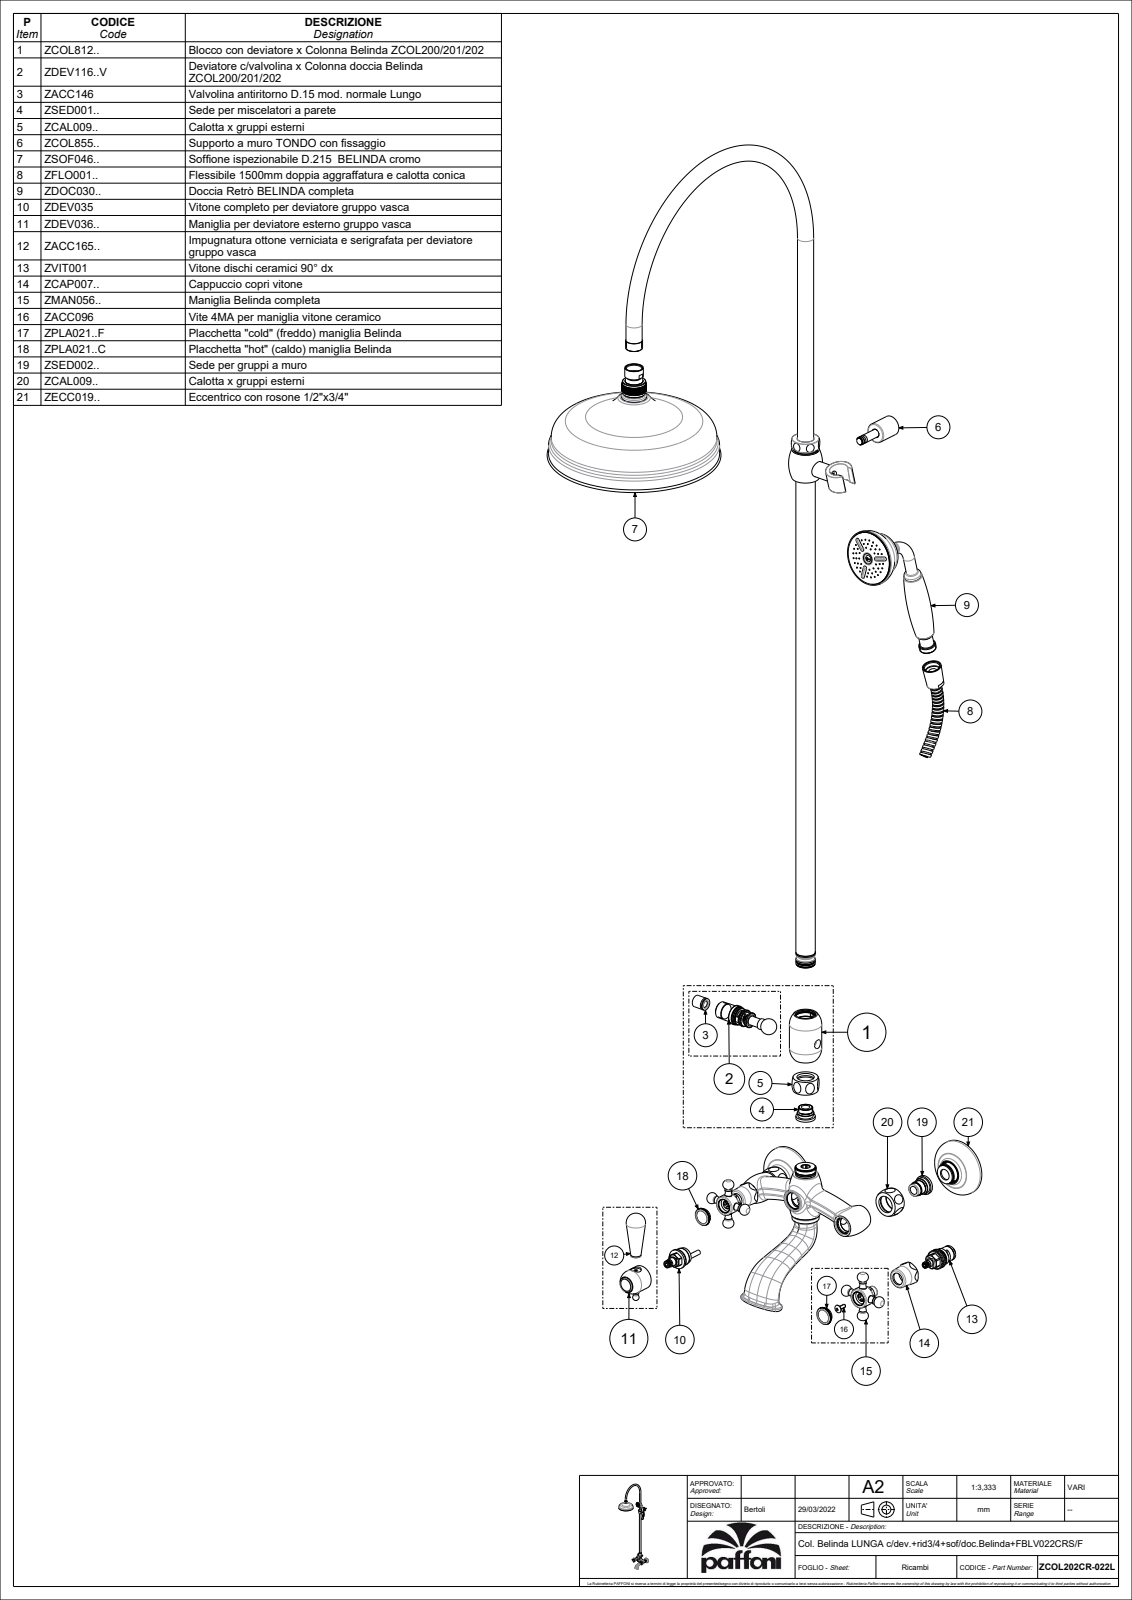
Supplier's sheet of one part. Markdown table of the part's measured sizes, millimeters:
| quantity | value |
| --- | --- |
| part name | ZCOL202CR-022L |
| STEP written by | CREO PARAMETRIC BY PTC INC, 2021404 (CONFIG_CONTROL_DESIGN) |
| units | millimeters |
| bodies | 0 solids, 1743 faces (344 planar, 431 cylindrical, 968 other) |
| overall size | 1401.19 × 512 × 220 |
| round holes (diameter × count) | 10.5 × 3, 24.1 × 3, 18 × 2, 18.63 × 2, 21 × 2, 21.5 × 2, 22.8 × 2, 25 × 2, 25.5 × 2, 27.5 × 2, 68 × 2, 11 × 1 |
| round bosses / shafts (diameter × count) | 21 × 4, 14 × 4, 70 × 2, 20 × 2, 16 × 2, 13 × 2, 7 × 2, 211.5 × 1 |
| partial cylindrical surfaces (radius × count) | 0.3 × 3, 3.04 × 2, 11 × 2, 44.47 × 2, 51.83 × 2, 91.42 × 2, 92.8 × 2, 13.75 × 1 |
| main face-to-face distances | 15, 23.5, 32, 3.5, 1, 27, 13.5, 44, 17, 33 |
| hole center spacings | 76.29, 76.3, 150, 330 |
